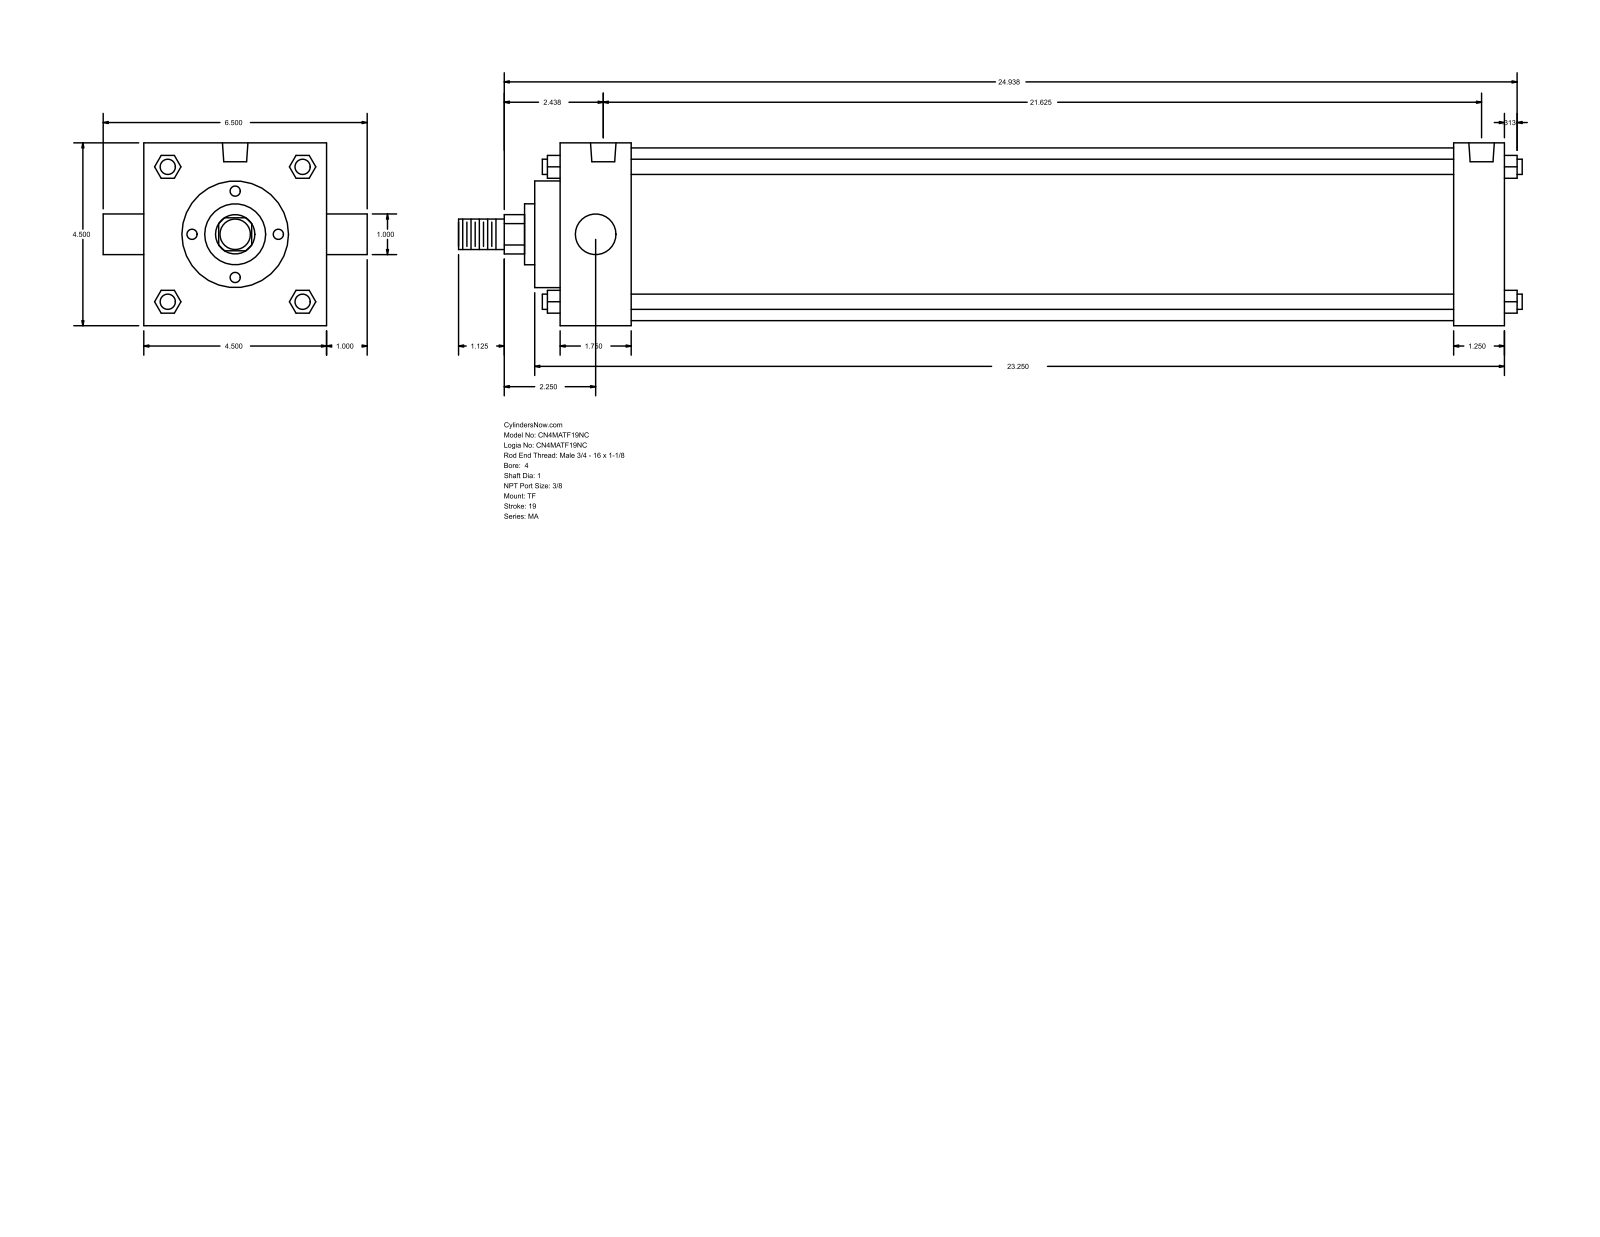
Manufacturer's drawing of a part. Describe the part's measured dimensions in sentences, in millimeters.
The part is named "MA_TF__0400_1". Its 3-D file was written by "GSSL Pune (CONFIG_CONTROL_DESIGN)". It is 0 solids with 122 faces: 93 planar, 29 cylindrical and 0 other. Overall it measures 665.16 by 165.1 by 114.3 millimeters. Round holes: 3 of diameter 11.11, 2 of diameter 15.93. Round bosses or shafts: 4 of diameter 9.53, 2 of diameter 25.4, 1 of diameter 107.95, 1 of diameter 66.67, 1 of diameter 38.1, 1 of diameter 19.05. Partial cylindrical surfaces (rounded edges, fillets, slot ends): 1 of radius 12.29. The main face-to-face distances are 114.3, 590.56, 558.81, 31.75, 44.46, 514.35, 546.1, 15.87, 60.33, 574.68. The hole center spacings are 4.76, 4.77, 539.75, 544.51, 544.52, 549.28.
